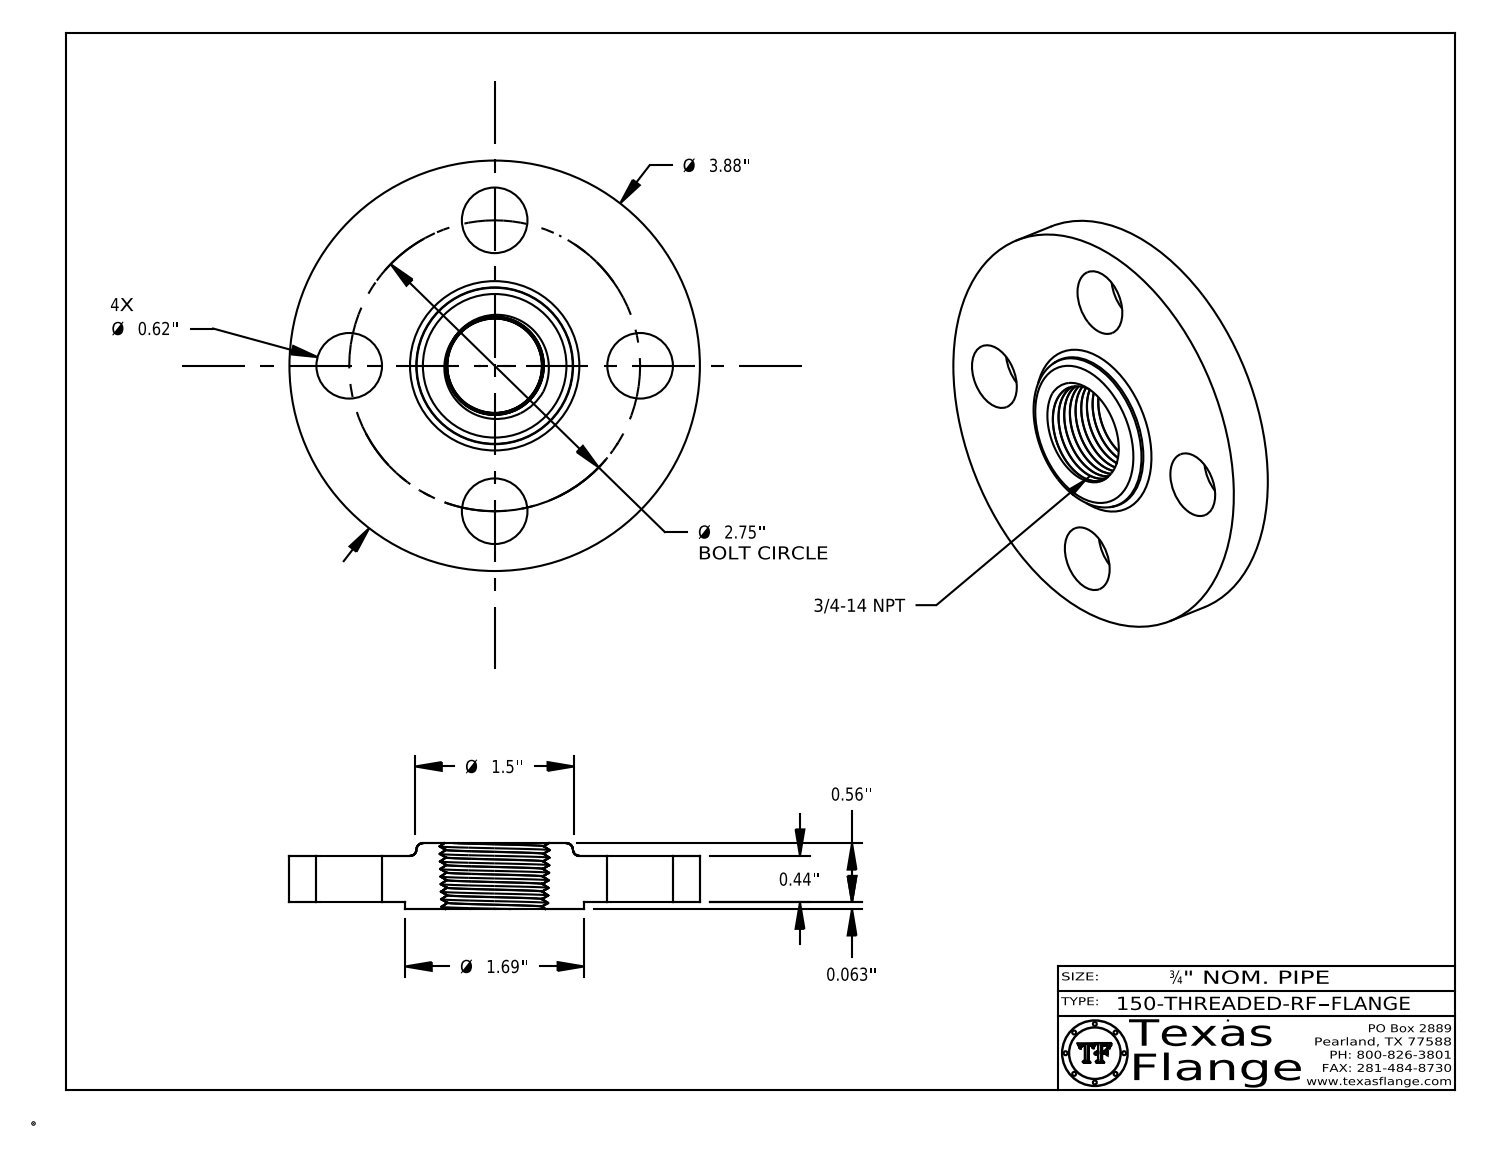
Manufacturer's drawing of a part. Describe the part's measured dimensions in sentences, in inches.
The part is named "150-THREADED-RF". Its 3-D file was written by "CATIA V5 STEP AP214 (AUTOMOTIVE_DESIGN)". It is 1 solid with 504 faces: 369 planar, 32 cylindrical and 103 other. Overall it measures 3.88 by 3.88 by 0.623 inches. Its volume is 4.56 cubic inches and its surface area 32.82 square inches. Round holes: 4 of diameter 0.62, 1 of diameter 0.495. Round bosses or shafts: 8 of diameter 0.03, 1 of diameter 3.88, 1 of diameter 1.69, 1 of diameter 0.39. The main face-to-face distances are 0.44, 0.063, 0.503, 0.622, 0.56, 0.12, 0.488, 0.425, 0.015, 0.135. The hole center spacings are 1.945, 1.052, 2.541, 2.75.
